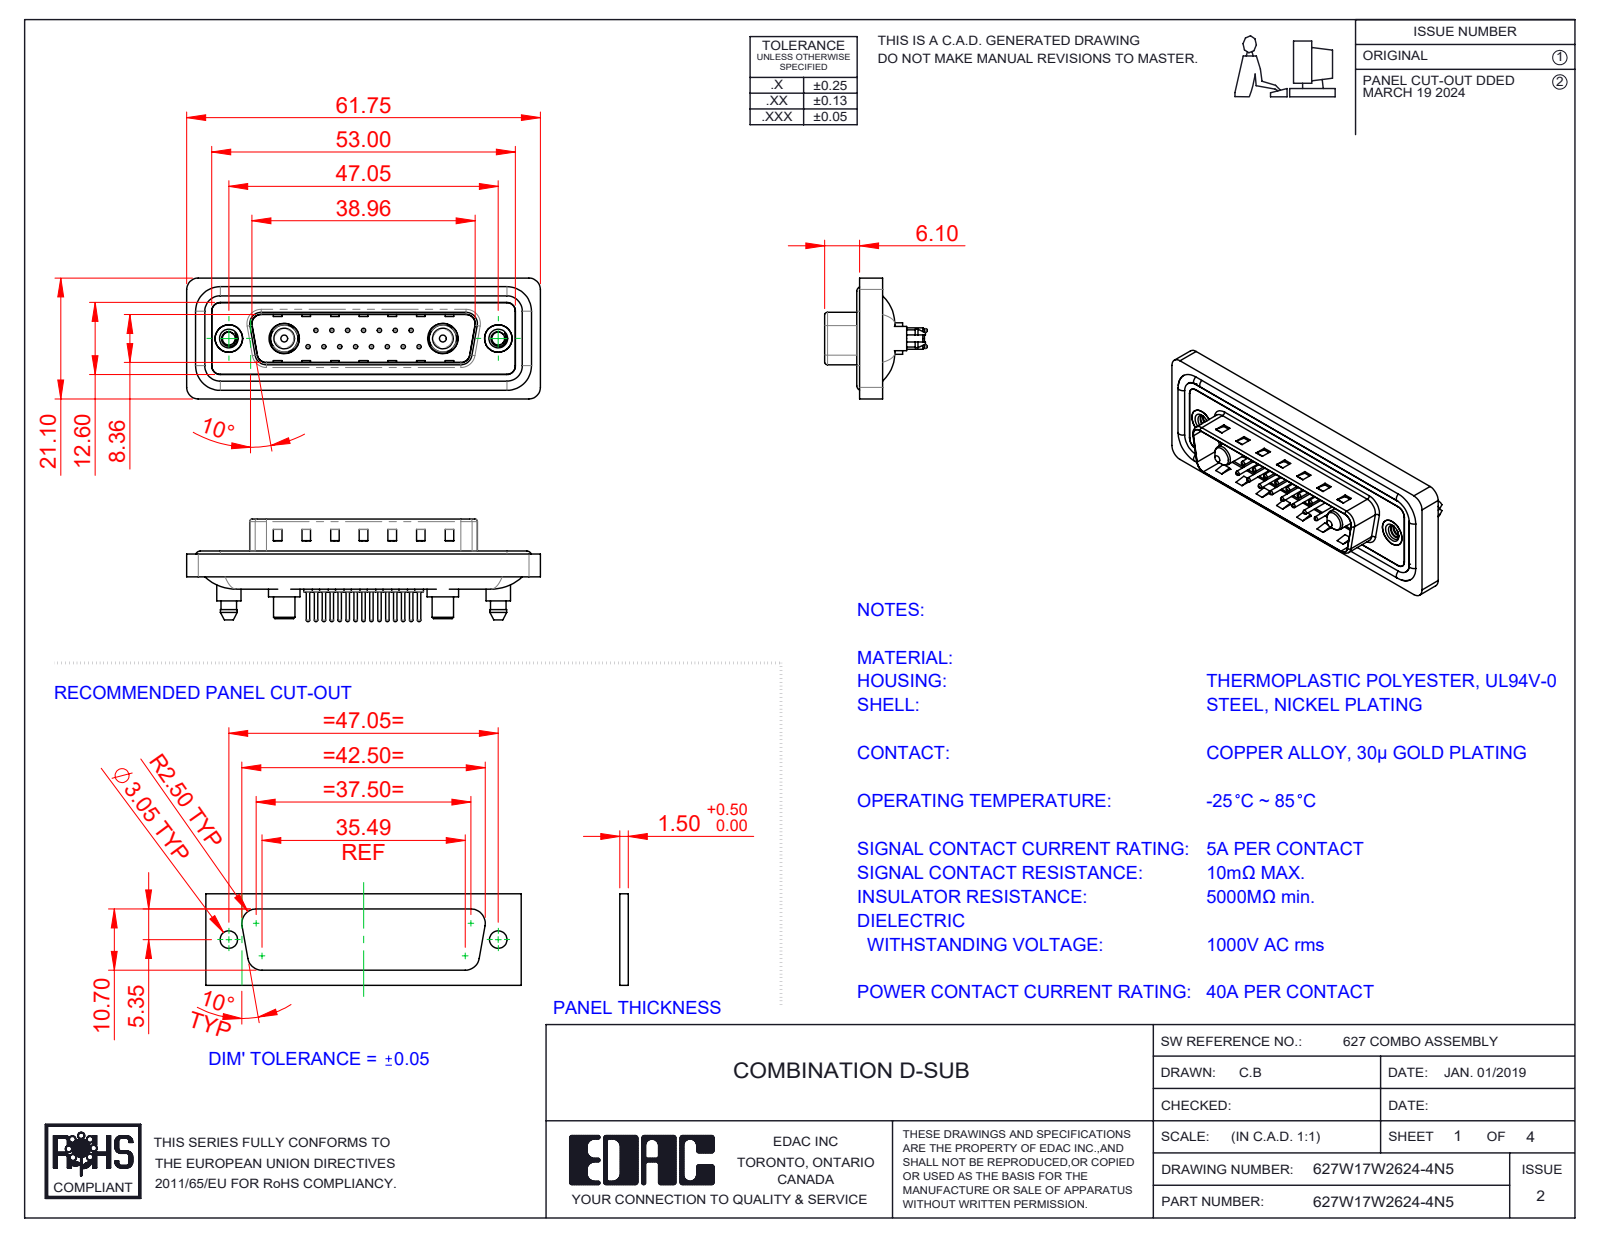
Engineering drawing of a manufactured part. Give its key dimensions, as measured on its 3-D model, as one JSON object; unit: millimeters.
{"part_name": "627Combo Threaded Boardlock_5; 627Combo Shell Front_25 Contacts; 627Combo Waterproof Housing_25 Contacts; 627Combo Housing_17W2 (+5 more)", "step_written_by": "SolidWorks 2023 (CONFIG_CONTROL_DESIGN)", "units": "millimeters", "bodies": {"solids": 26, "faces": 1166, "planar": 350, "cylindrical": 468, "other": 348}, "overall_size": [61.75, 21.1, 17.9], "volume_mm3": 7437, "surface_area_mm2": 12269, "round_holes": [[0.75, 15], [1.6, 15], [2, 15], [2.26, 2], [4, 2], [4.8, 2], [4.85, 2], [5, 2], [5.3, 2]], "round_bosses_or_shafts": [[1.5, 15], [0.6, 15], [1.6, 4], [5.5, 2], [5.4, 2], [5.2, 2], [4.9, 2], [4.75, 2]], "partial_cylinders_radius": [[1.5, 24], [2, 18], [1.6, 10], [0.5, 8], [0.25, 4], [0.6, 4], [0.65, 4], [0.9, 4]], "face_to_face_distances": [0.4, 1.5, 1.1, 1.6, 0.5, 3.1, 2.9, 0.82, 9.58, 4.1], "hole_center_spacings": [3.16, 2.77, 5.54, 8.31, 5.04, 7.49, 11.08, 5.03]}
